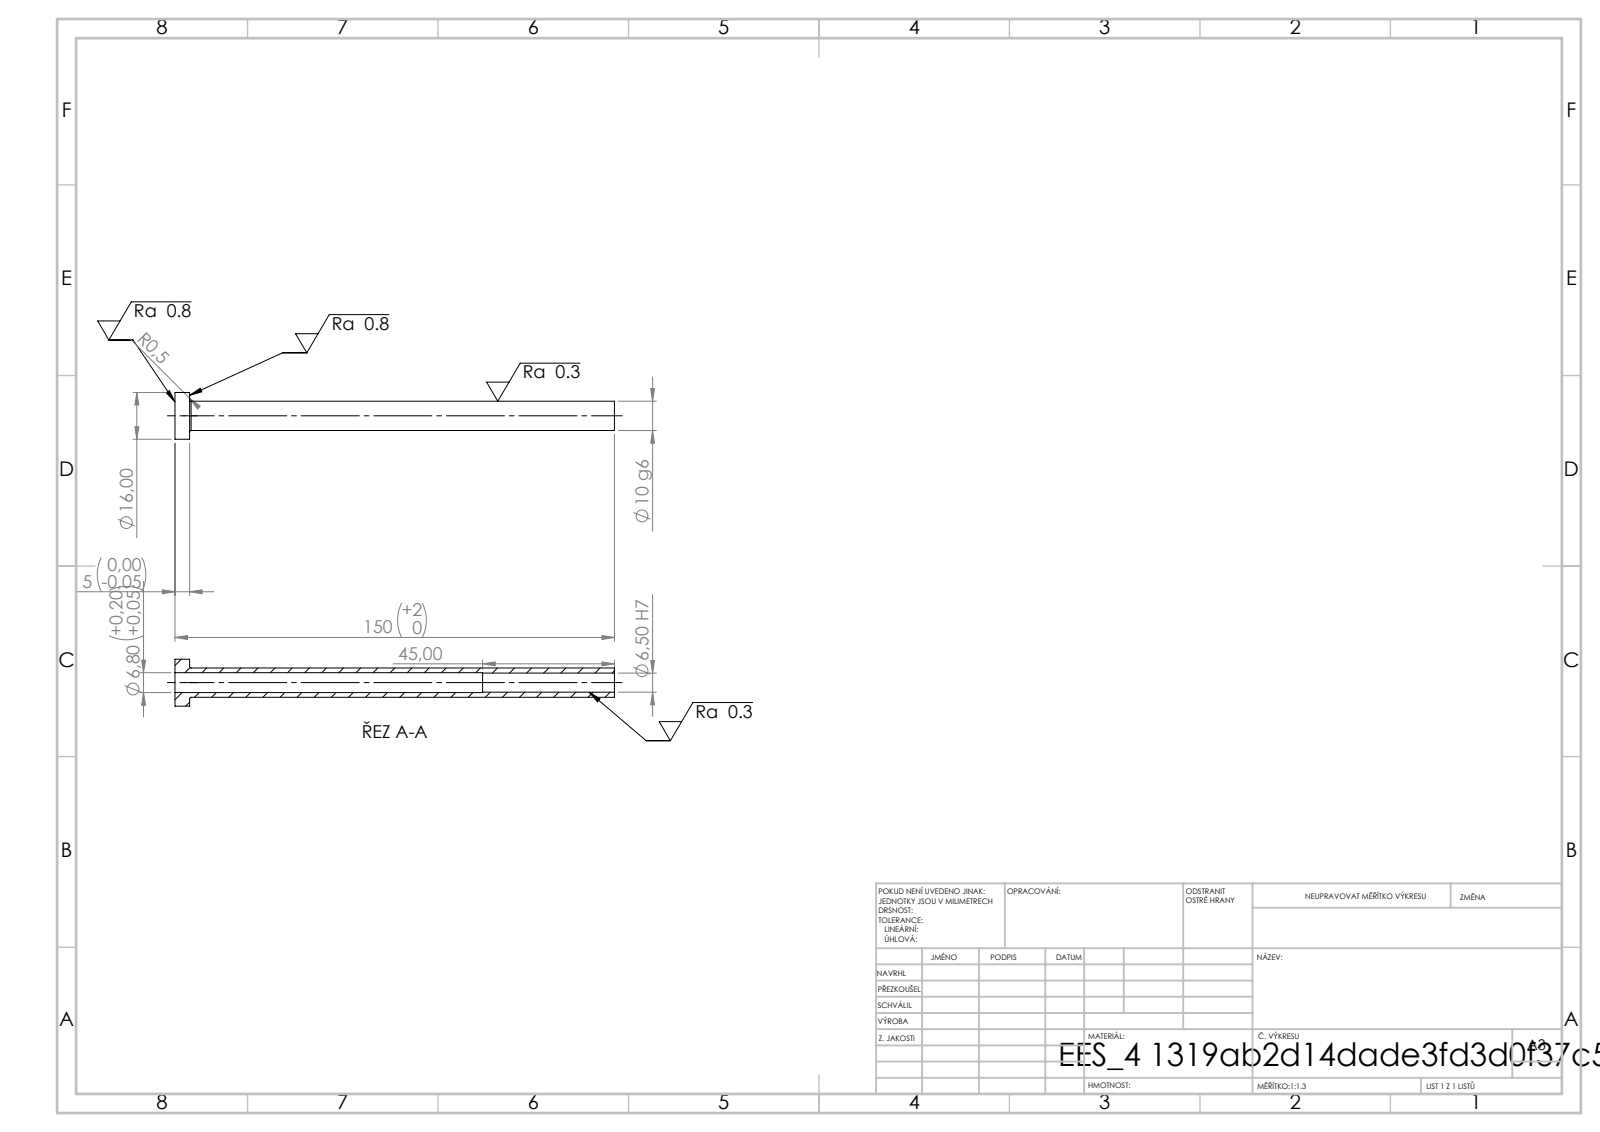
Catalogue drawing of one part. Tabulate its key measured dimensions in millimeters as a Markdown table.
| quantity | value |
| --- | --- |
| STEP written by | SolidWorks 2019 (CONFIG_CONTROL_DESIGN) |
| units | millimeters |
| bodies | 1 solid, 14 faces (4 planar, 8 cylindrical, 2 other) |
| overall size | 150 × 16 × 16 |
| volume | 7 089 mm³ |
| surface area | 8 298 mm² |
| round holes (diameter × count) | 6.5 × 1, 6.8 × 1 |
| round bosses / shafts (diameter × count) | 16 × 1, 10 × 1 |
| main face-to-face distances | 5, 150, 145, 105, 100, 45 |
